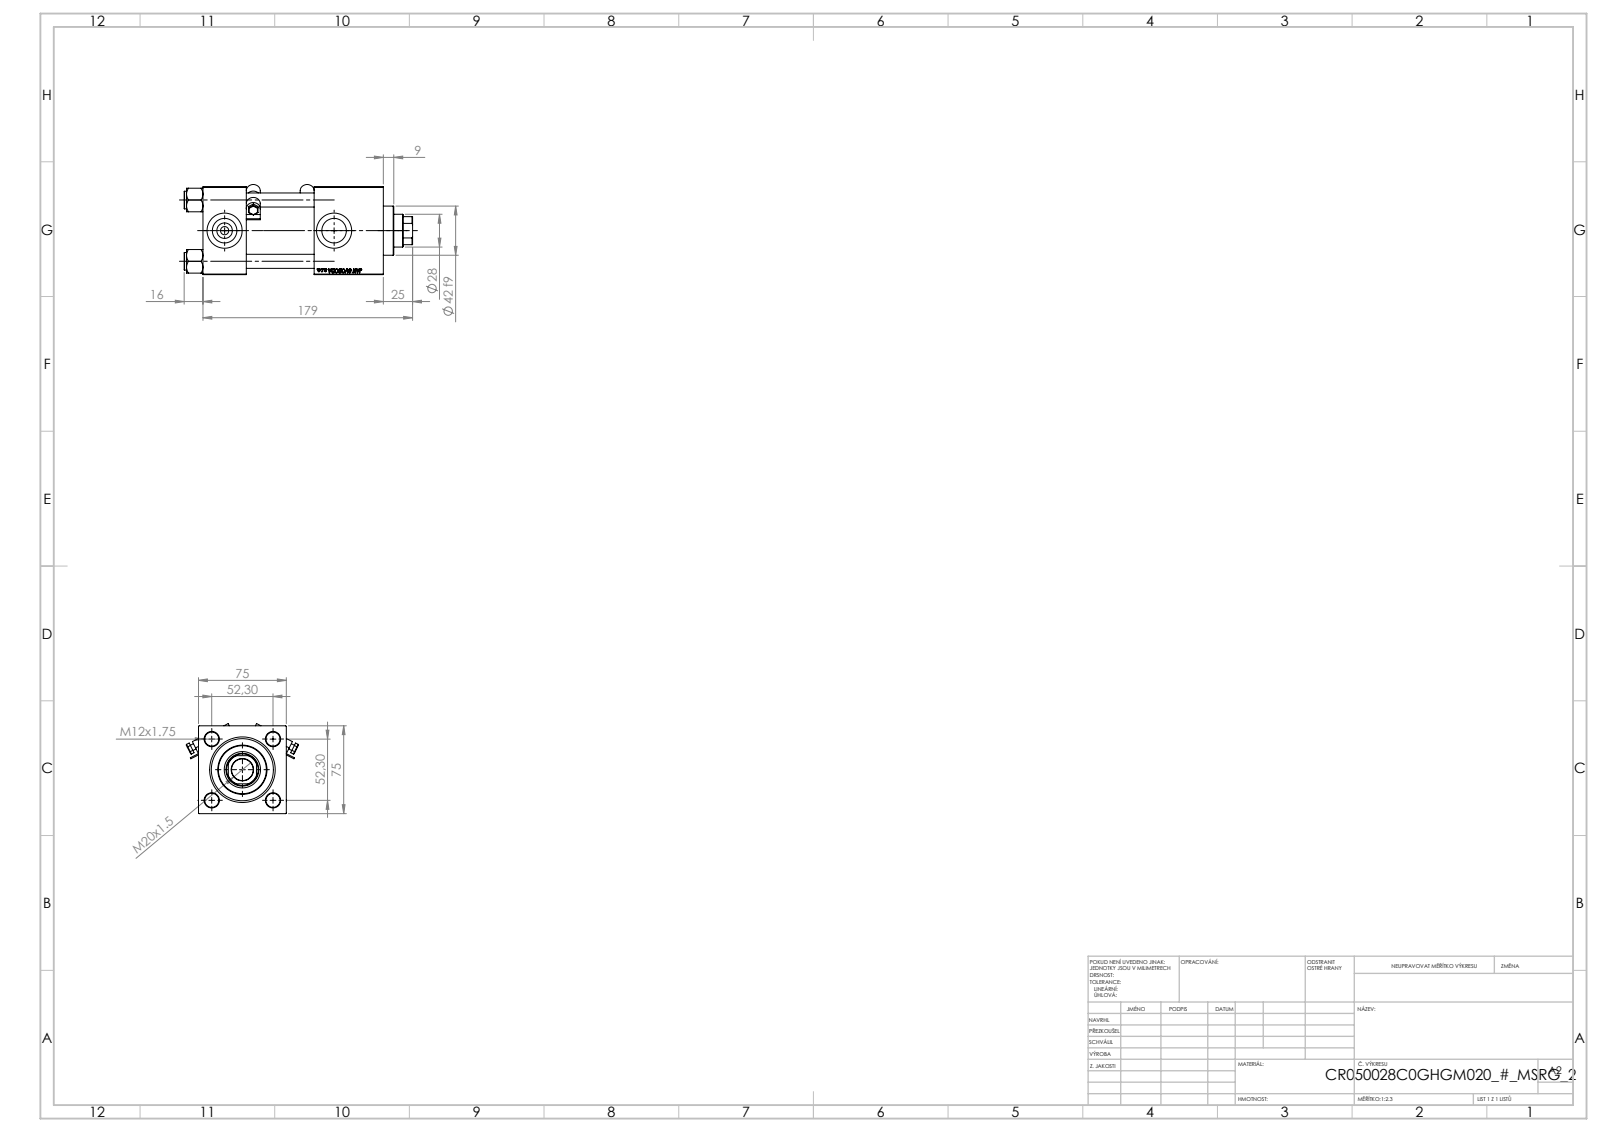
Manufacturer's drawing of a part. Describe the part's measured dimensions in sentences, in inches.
The part is named "V215CR_VCP_C; V215CR_C_Body; V215CR_C_TYCINKA; NUT_M5_C (+2 more)". Its 3-D file was written by "SolidWorks 2019 (CONFIG_CONTROL_DESIGN)". It is 13 solids with 1212 faces: 562 planar, 114 cylindrical and 536 other. Overall it measures 7.677 by 3.772 by 3.027 inches. Its volume is 41.28 cubic inches and its surface area 240.9 square inches. Round holes: 4 of diameter 0.472, 2 of diameter 0.276, 2 of diameter 0.825, 2 of diameter 1.181, 1 of diameter 0.728, 1 of diameter 1.102, 1 of diameter 1.22, 1 of diameter 1.614, 1 of diameter 1.969, 1 of diameter 2.087. Round bosses or shafts: 4 of diameter 0.591, 2 of diameter 0.197, 2 of diameter 0.098, 1 of diameter 2.205, 1 of diameter 1.654. Partial cylindrical surfaces (rounded edges, fillets, slot ends): 12 of radius 0.02, 4 of radius 0.236, 1 of radius 0.531. The main face-to-face distances are 2.953, 1.457, 2.323, 3.74, 2.283, 6.063, 4.606, 4.933, 3.476, 1.193. The hole center spacings are 1.456, 2.059, 2.912, 3.681.
